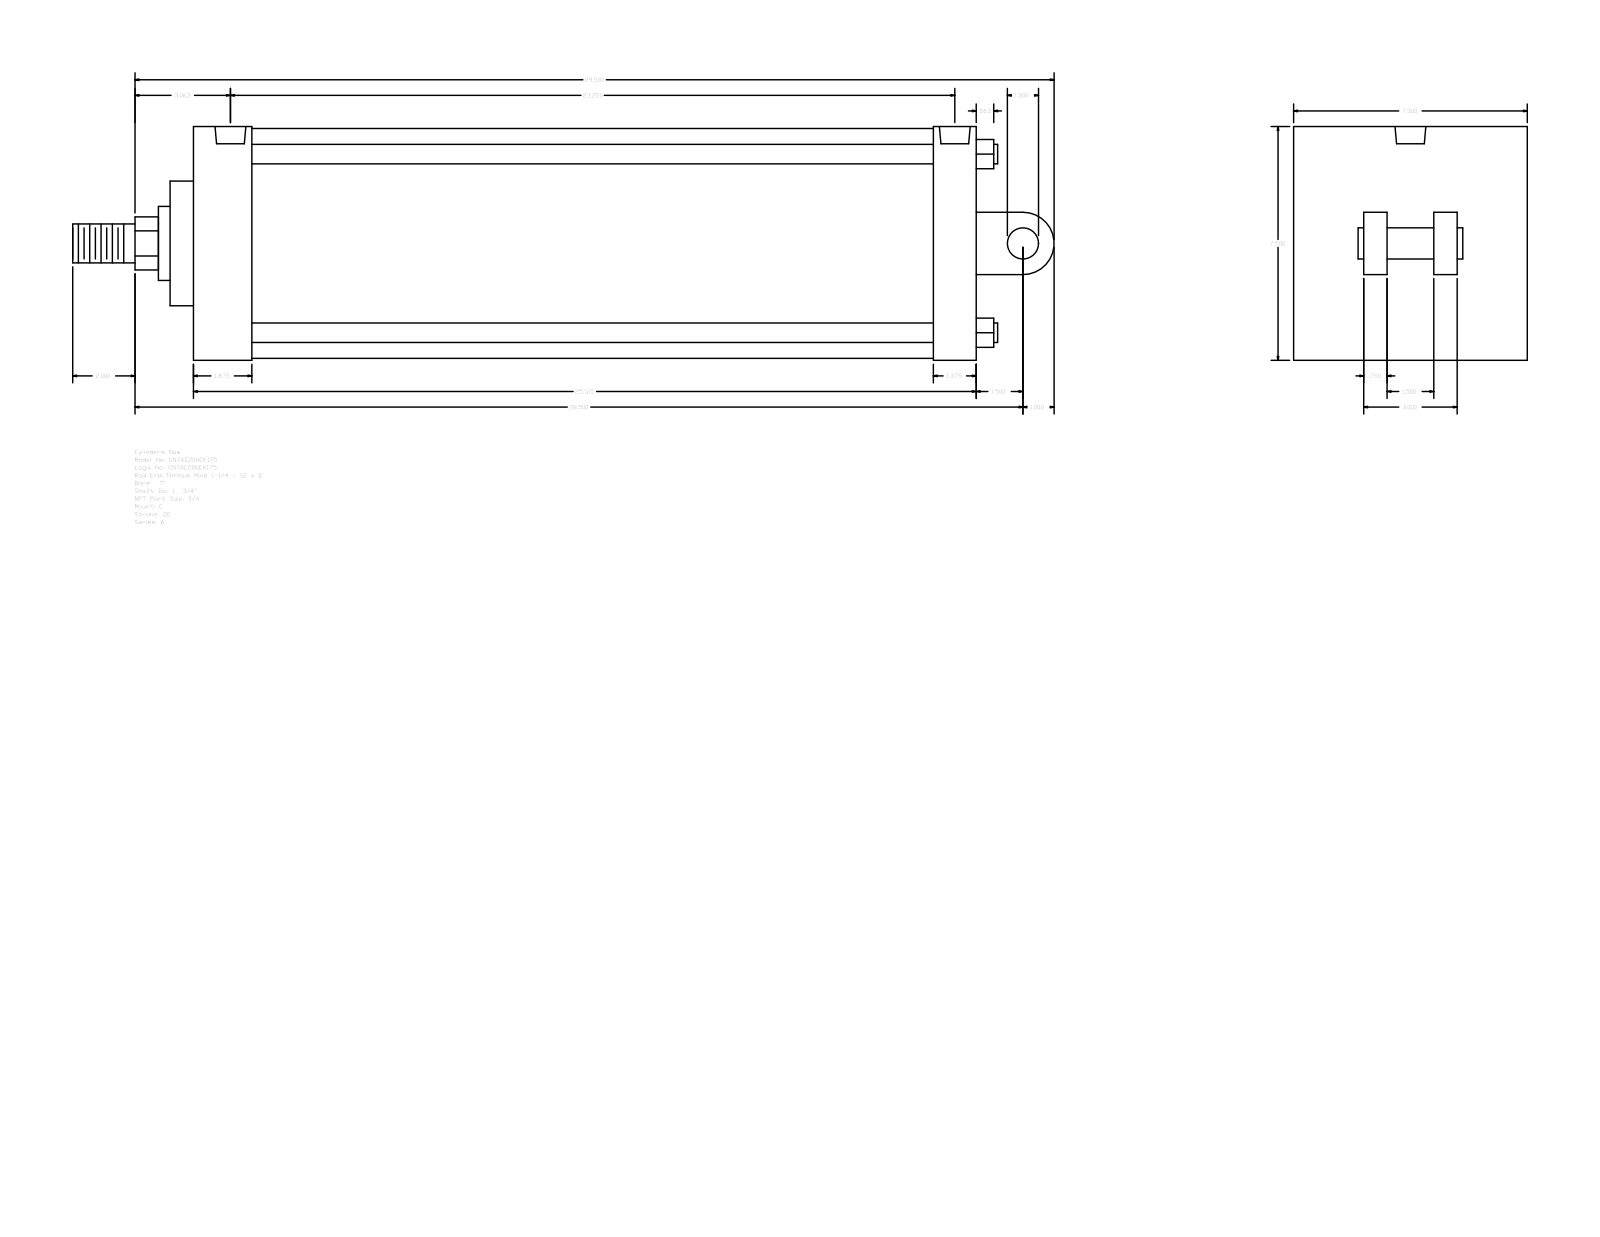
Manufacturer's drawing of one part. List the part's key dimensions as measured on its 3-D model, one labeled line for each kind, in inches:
Part name (STEP PRODUCT): A_C__0700_1.75
STEP written by: GSSL Pune (CONFIG_CONTROL_DESIGN)
Units: inches
Bodies: 0 solids, 104 faces (75 planar, 29 cylindrical, 0 other)
Overall size (bounding box): 31.5 × 7.5 × 7.5
Round holes (diameter × count): ⌀0.594 ×4, ⌀0.989 ×2
Round bosses / shafts (diameter × count): ⌀0.625 ×4, ⌀7.375 ×1, ⌀2.375 ×1, ⌀1.75 ×1, ⌀1.25 ×1, ⌀1 ×1
Partial cylindrical surfaces — rounded edges, fillets, slot ends (radius × count): R0.852 ×1, R1 ×1
Main face-to-face distances: 7.5, 25.125, 0.75, 3, 2.25, 5.75, 1.75, 2.75, 1.875, 23.25
Hole centre spacings: 0.219, 22.812, 23.031, 23.25
